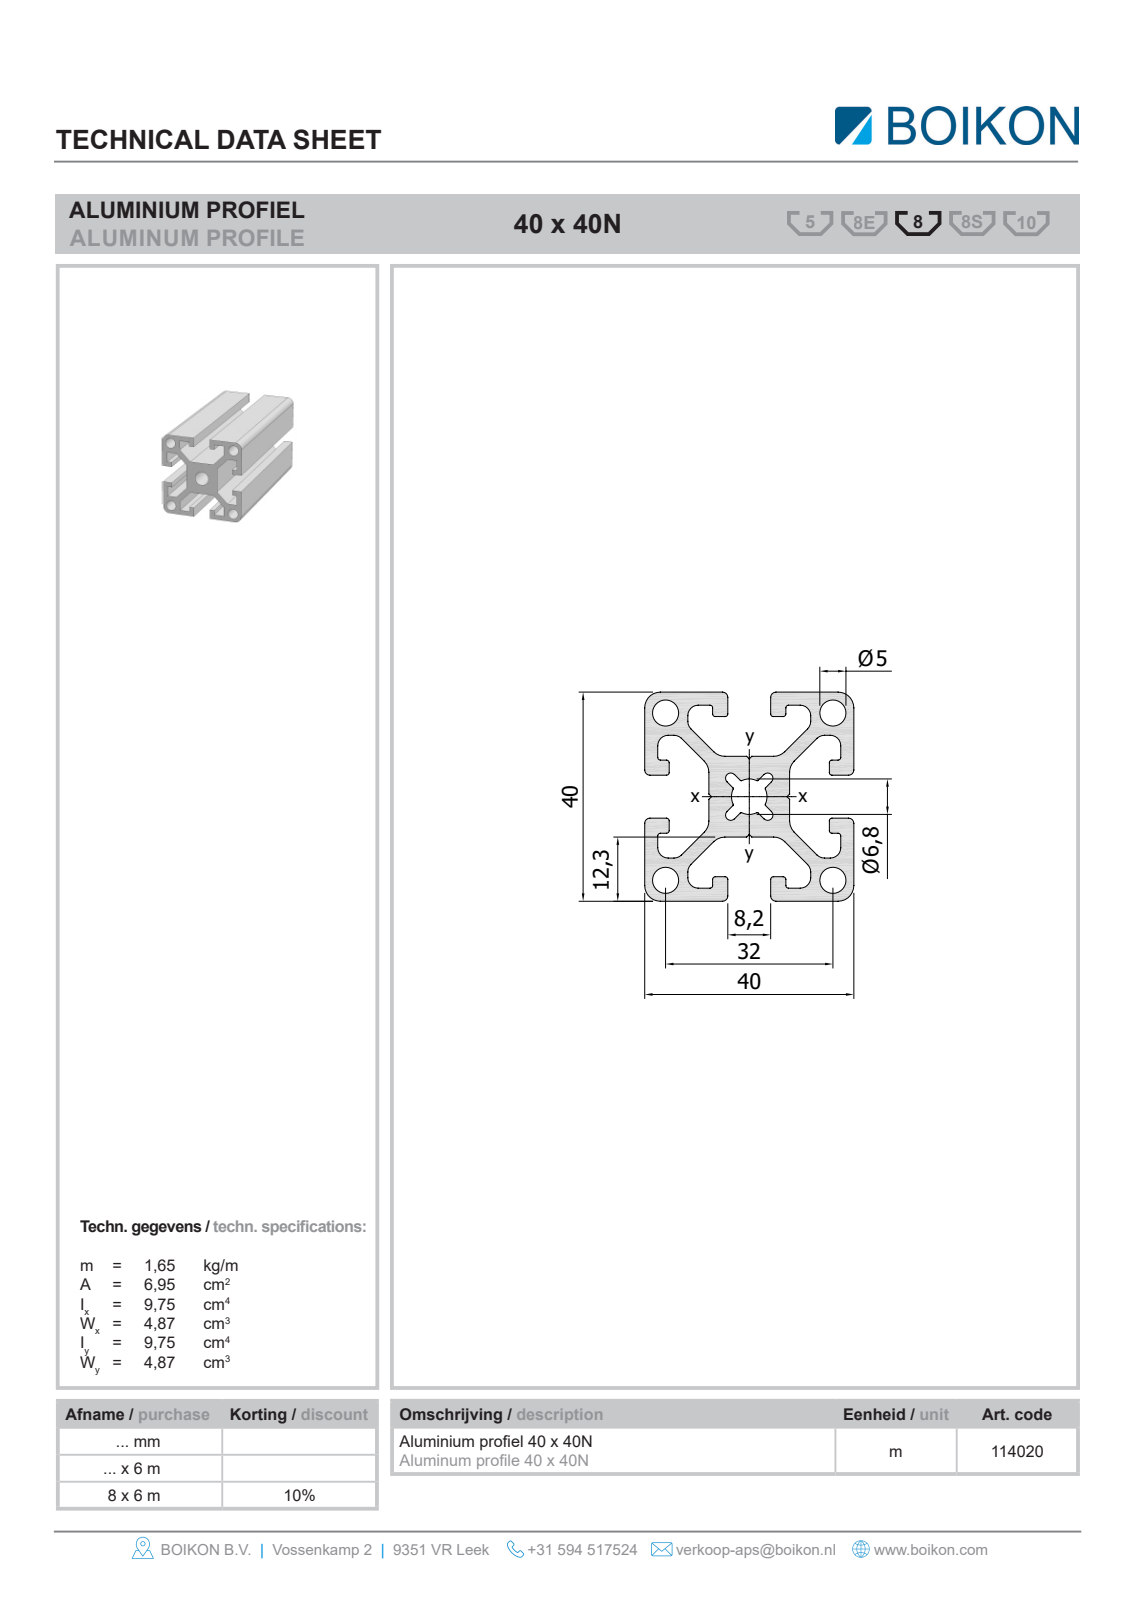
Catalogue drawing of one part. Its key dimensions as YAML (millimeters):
part_name: "Root; 11402040x40NBOIKON0"
step_written_by: "HiCAD 2013 1802.4 Build 509 (AUTOMOTIVE_DESIGN)"
units: millimeters
bodies: {solids: 1, faces: 71, planar: 62, cylindrical: 9, other: 0}
overall_size: [1000, 40, 40]
volume: 661155
surface_area: 463418
round_holes:
  - {diameter: 5, count: 4}
  - {diameter: 6.8, count: 1}
partial_cylinders:
  - {radius: 3, count: 4}
face_to_face_distances: [2.25, 13.65, 24.1, 21.85, 40, 12.25, 27.75, 37.75, 10, 25.5]
hole_center_spacings: [22.63, 32, 45.25]
